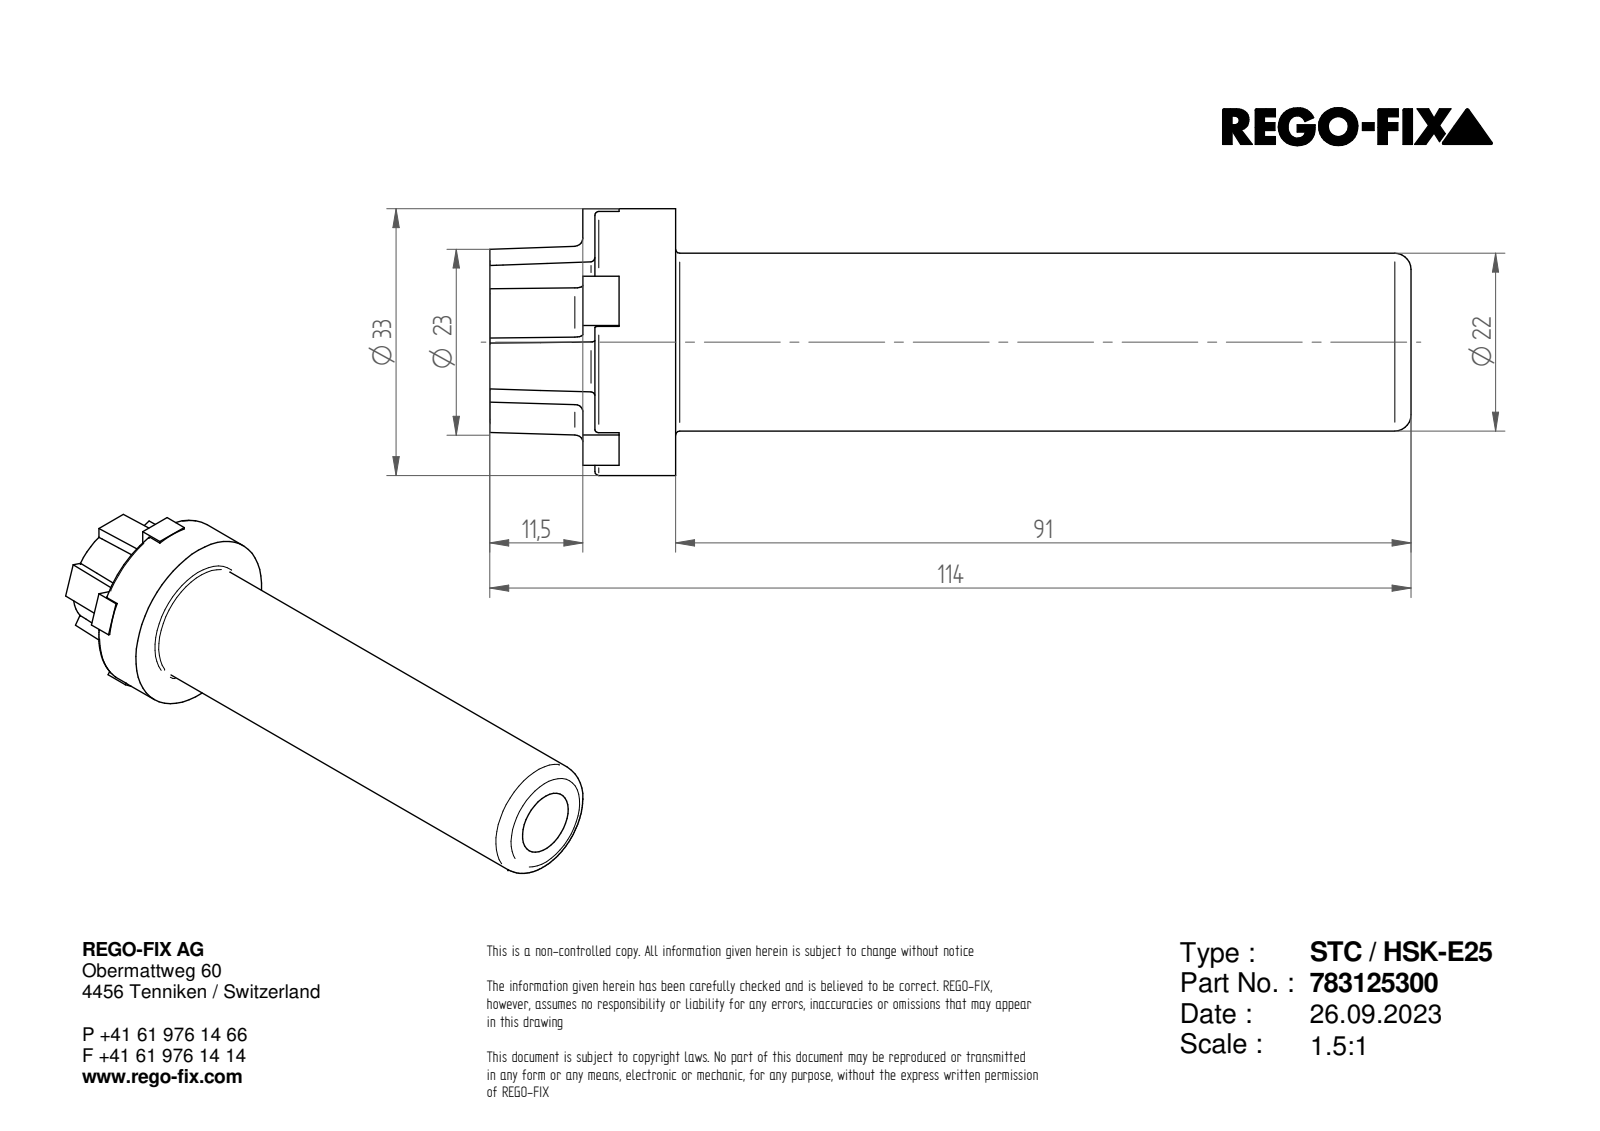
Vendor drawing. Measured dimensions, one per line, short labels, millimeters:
name: 0029423
written by: ST-DEVELOPER v16.7 (AUTOMOTIVE_DESIGN)
unit: mm
bodies: 1 solid, 75 faces (44 planar, 9 cylindrical, 22 other)
size: 114 × 33.38 × 33.01
volume: 34 624 mm³; area: 14 267 mm²
holes: 1× ⌀12, 1× ⌀14
bosses: 1× ⌀33, 1× ⌀22
rounds: 5× R1
face distances: 10, 11.5, 6.4, 13, 23, 114, 101, 91, 1.5, 102.5
